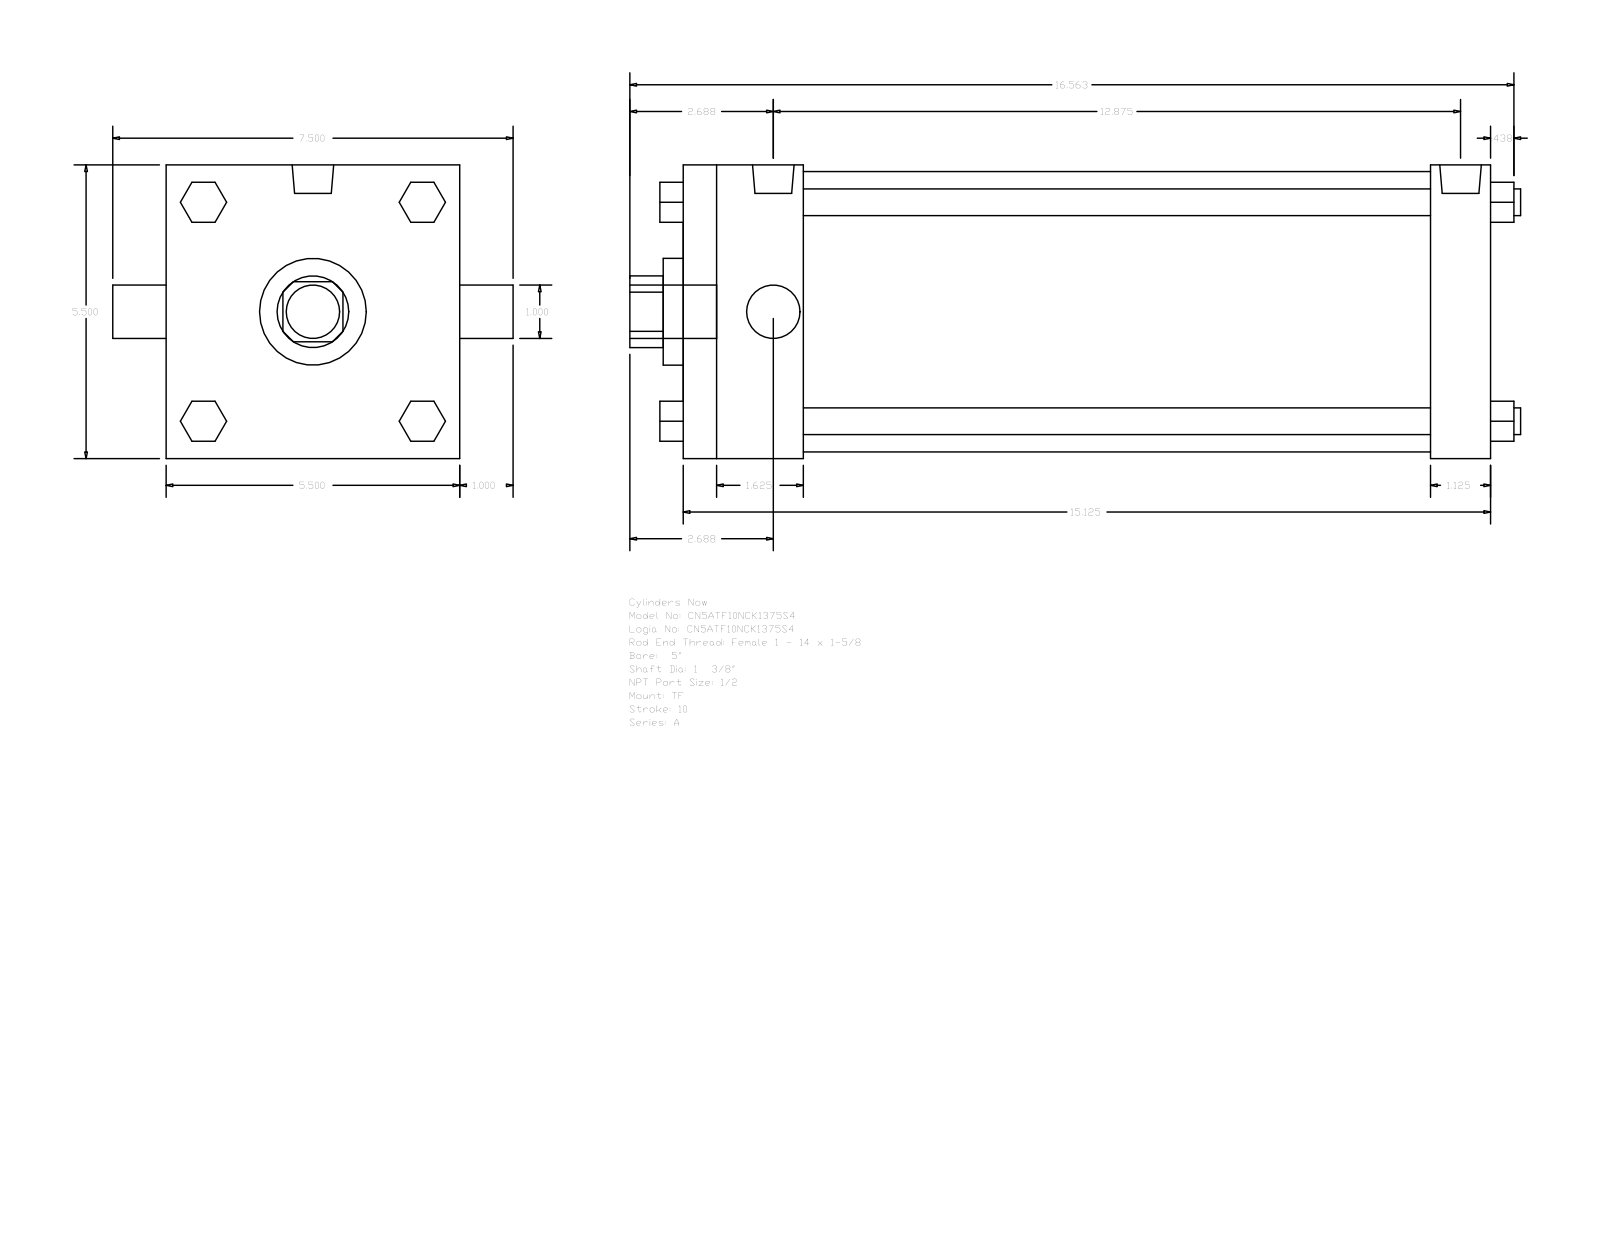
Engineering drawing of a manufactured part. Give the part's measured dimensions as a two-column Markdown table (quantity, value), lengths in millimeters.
| quantity | value |
| --- | --- |
| part name | A_TF__0500_1.375 |
| STEP written by | GSSL Pune (CONFIG_CONTROL_DESIGN) |
| units | millimeters |
| bodies | 0 solids, 120 faces (92 planar, 28 cylindrical, 0 other) |
| overall size | 423.86 × 190.5 × 139.7 |
| round holes (diameter × count) | 25.4 × 1, 34.92 × 1, 50.8 × 1, 133.35 × 1 |
| round bosses / shafts (diameter × count) | 12.7 × 4, 8.73 × 3, 19.77 × 2, 25.4 × 1 |
| partial cylindrical surfaces (radius × count) | 17.06 × 1 |
| main face-to-face distances | 139.7, 384.17, 28.57, 355.6, 57.15, 298.45, 327.02, 19.05, 52.07, 90.18 |
